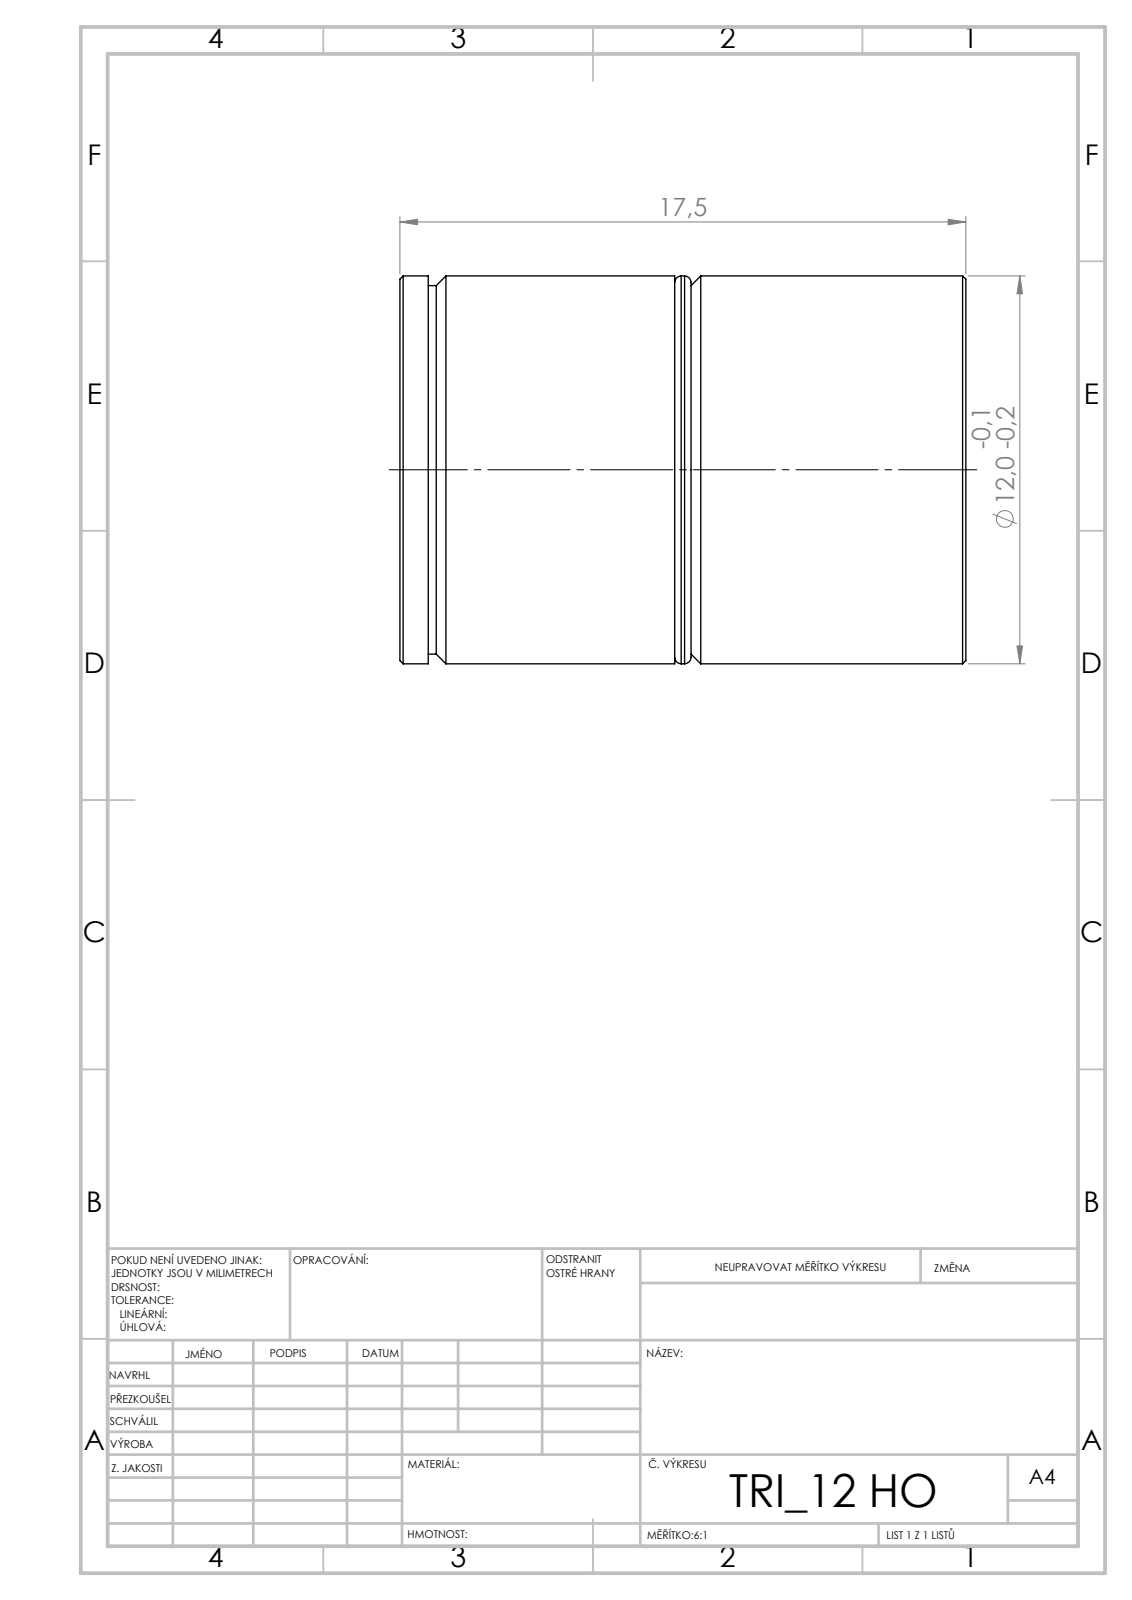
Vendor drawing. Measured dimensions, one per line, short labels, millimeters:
written by: SolidWorks 2019 (CONFIG_CONTROL_DESIGN)
unit: mm
bodies: 2 solids, 37 faces (13 planar, 12 cylindrical, 12 other)
size: 17.5 × 12 × 12
volume: 1 933 mm³; area: 1 185 mm²
bosses: 1× ⌀12, 1× ⌀11.4
face distances: 8.5, 9, 0.5, 7.5, 8, 16.5, 1, 17.5, 10.2, 16.63
